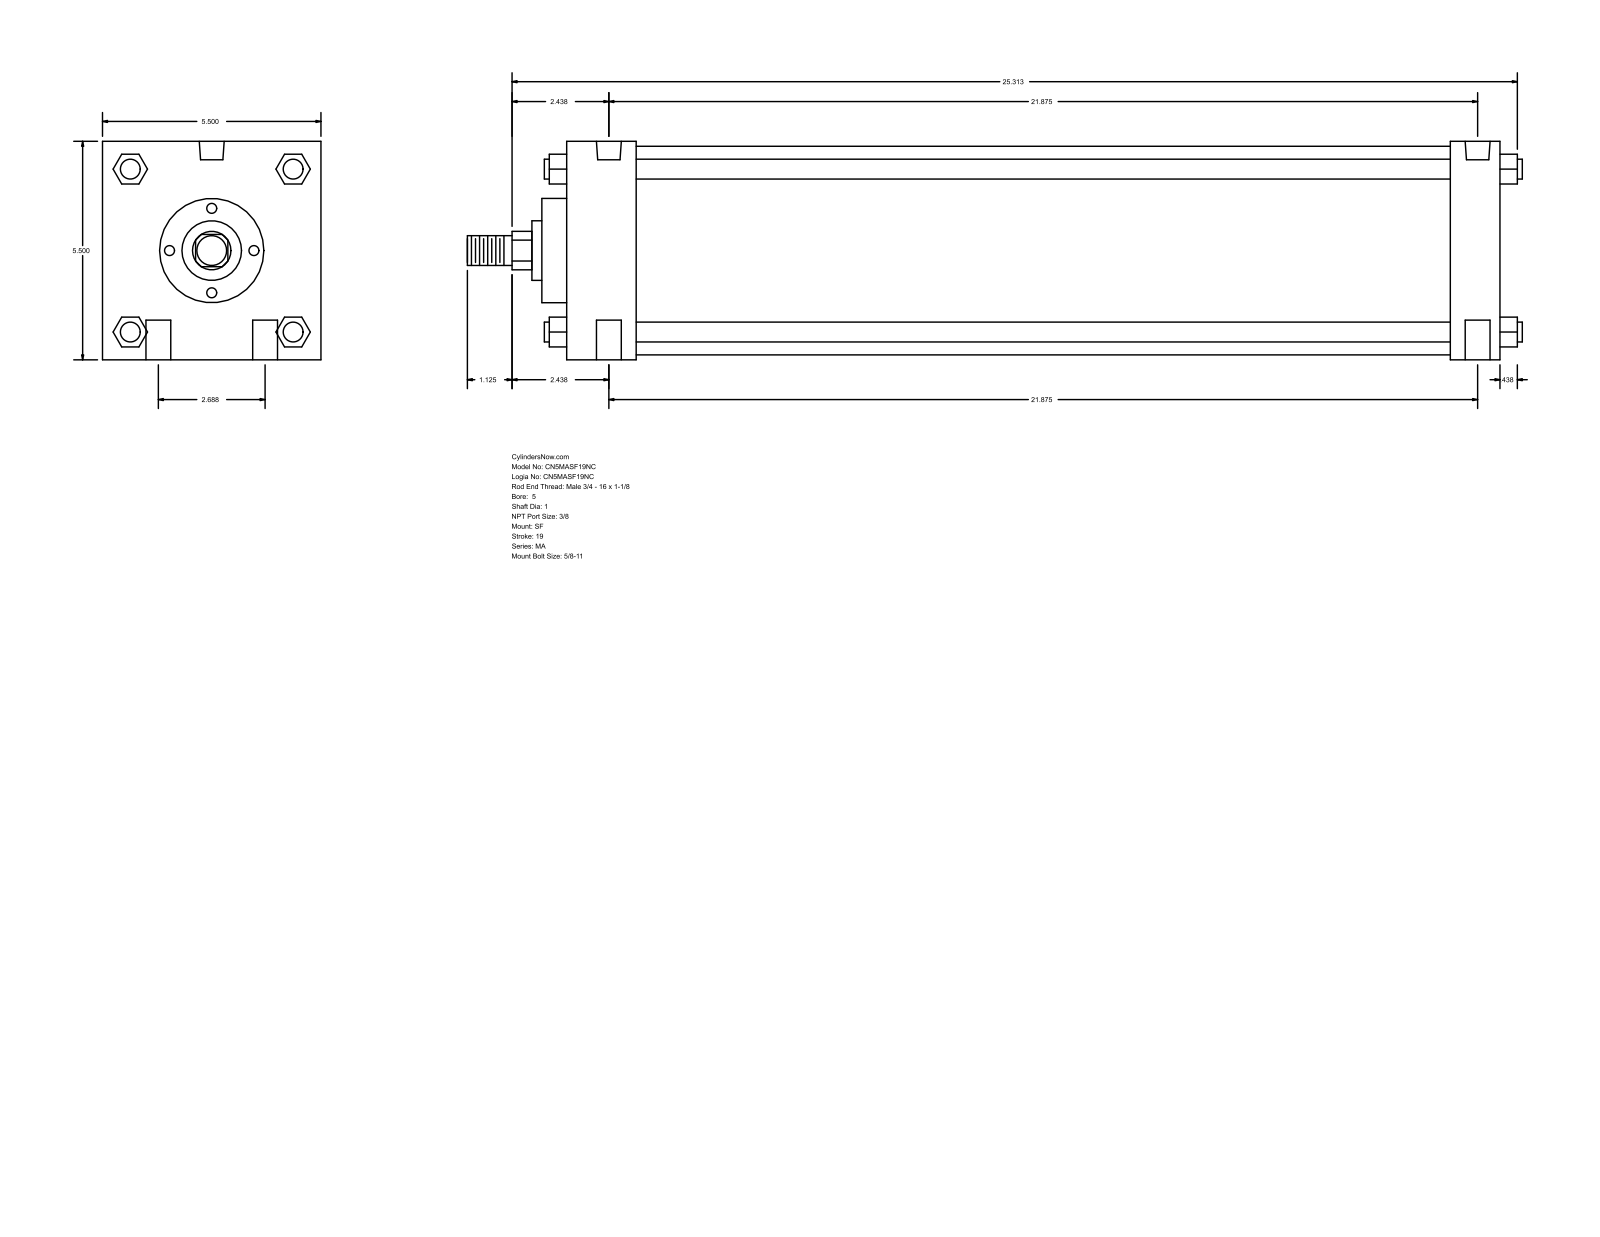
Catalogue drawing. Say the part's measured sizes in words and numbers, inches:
The part is named "MA_SF__0500_1". Its 3-D file was written by "GSSL Pune (CONFIG_CONTROL_DESIGN)". It is 0 solids with 126 faces: 95 planar, 31 cylindrical and 0 other. Overall it measures 26.563 by 5.5 by 5.5 inches. Round holes: 4 of diameter 0.625, 2 of diameter 0.437, 2 of diameter 0.627. Round bosses or shafts: 4 of diameter 0.5, 1 of diameter 5.25, 1 of diameter 2.625, 1 of diameter 1.5, 1 of diameter 1, 1 of diameter 0.75. Partial cylindrical surfaces (rounded edges, fillets, slot ends): 1 of radius 0.484. The main face-to-face distances are 5.5, 23.5, 1.75, 22.25, 20.5, 21.75, 1.25, 0.625, 2.375, 22.875. The hole center spacings are 1.344, 21.917, 21.875, 2.687, 22.04, 21.5.
